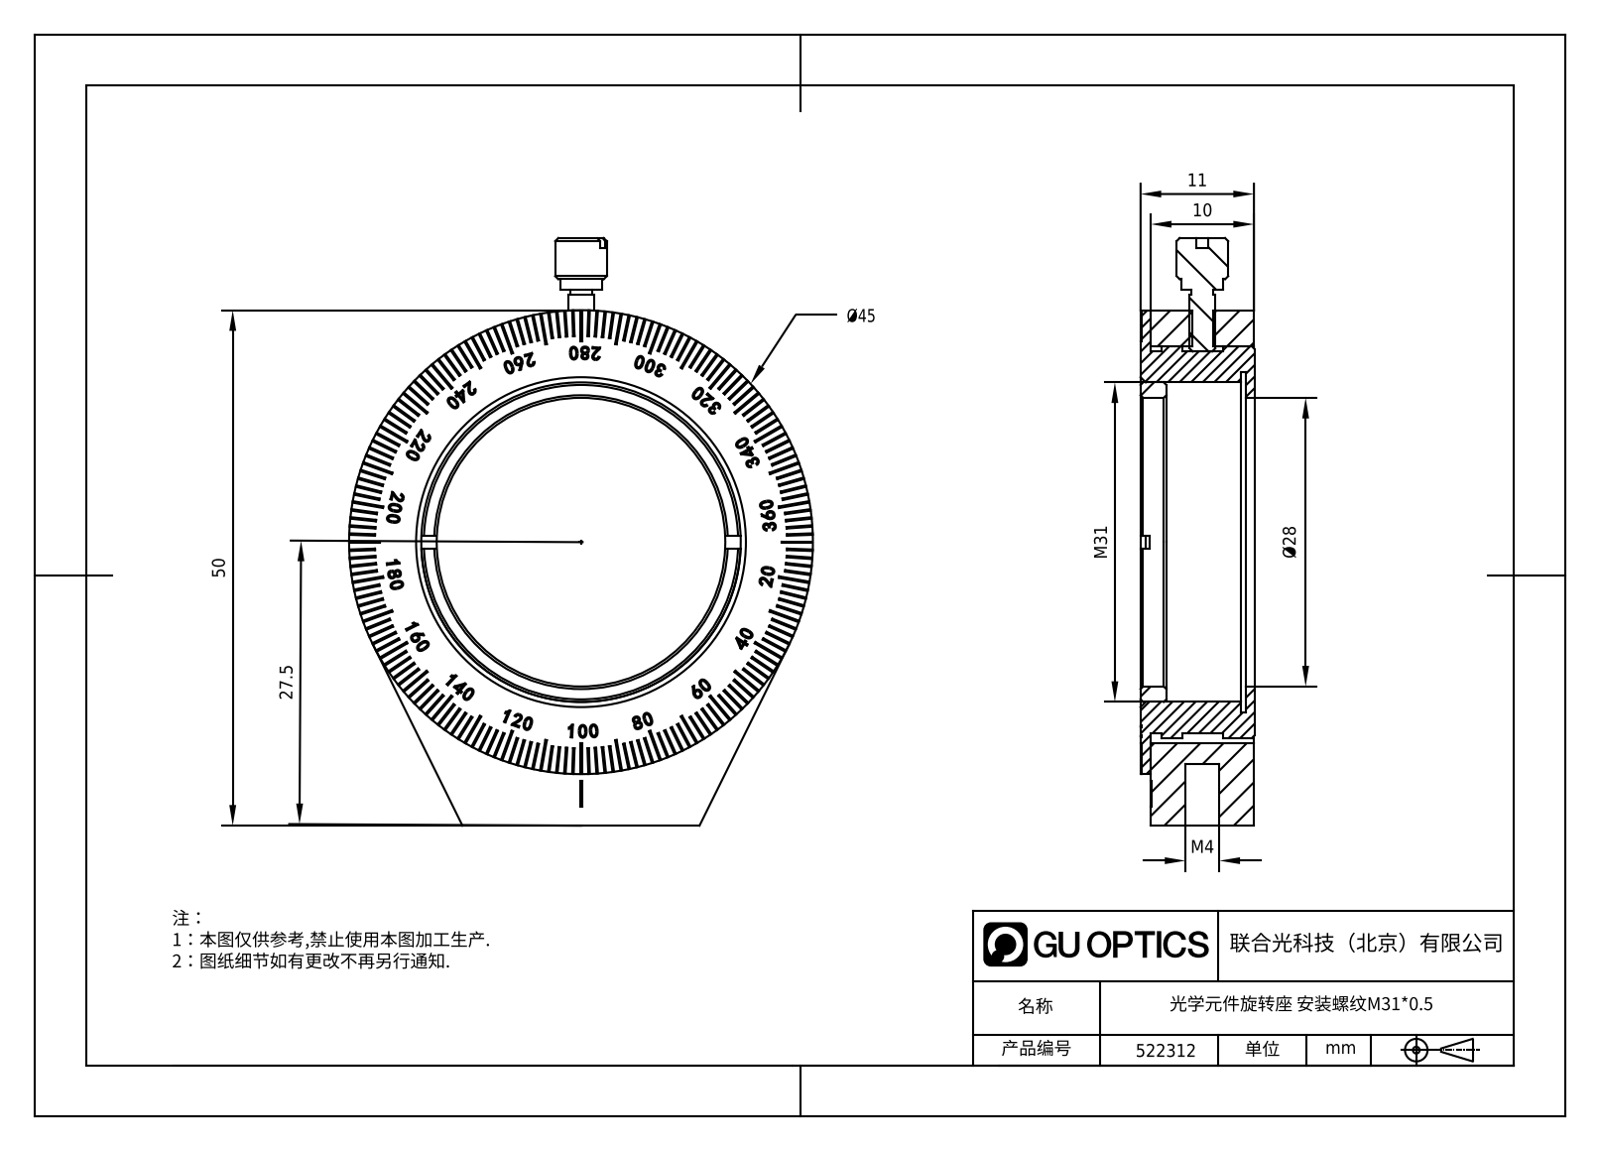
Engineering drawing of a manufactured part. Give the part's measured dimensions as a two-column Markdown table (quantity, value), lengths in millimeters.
| quantity | value |
| --- | --- |
| part name | 522312; 一体式手拧螺丝_30.13.2.2.3-SNTY-M2.5x6-0511; ZFK透镜卡环压圈_1.8.5.16-ZFK-K30 |
| STEP written by | SolidWorks 2020 (CONFIG_CONTROL_DESIGN) |
| units | millimeters |
| bodies | 4 solids, 1197 faces (992 planar, 19 cylindrical, 186 other) |
| overall size | 57 × 45 × 11.05 |
| volume | 11 168 mm³ |
| surface area | 9 803 mm² |
| round holes (diameter × count) | 2.05 × 1, 3.3 × 1, 28 × 1, 31 × 1, 33 × 1 |
| round bosses / shafts (diameter × count) | 45 × 1, 38 × 1, 37 × 1, 5 × 1, 4 × 1, 2.5 × 1, 2.1 × 1 |
| partial cylindrical surfaces (radius × count) | 18 × 1 |
| main face-to-face distances | 1, 10, 11, 10.05, 11.05, 0.8, 0.75, 9.25, 10.25, 0.5 |
